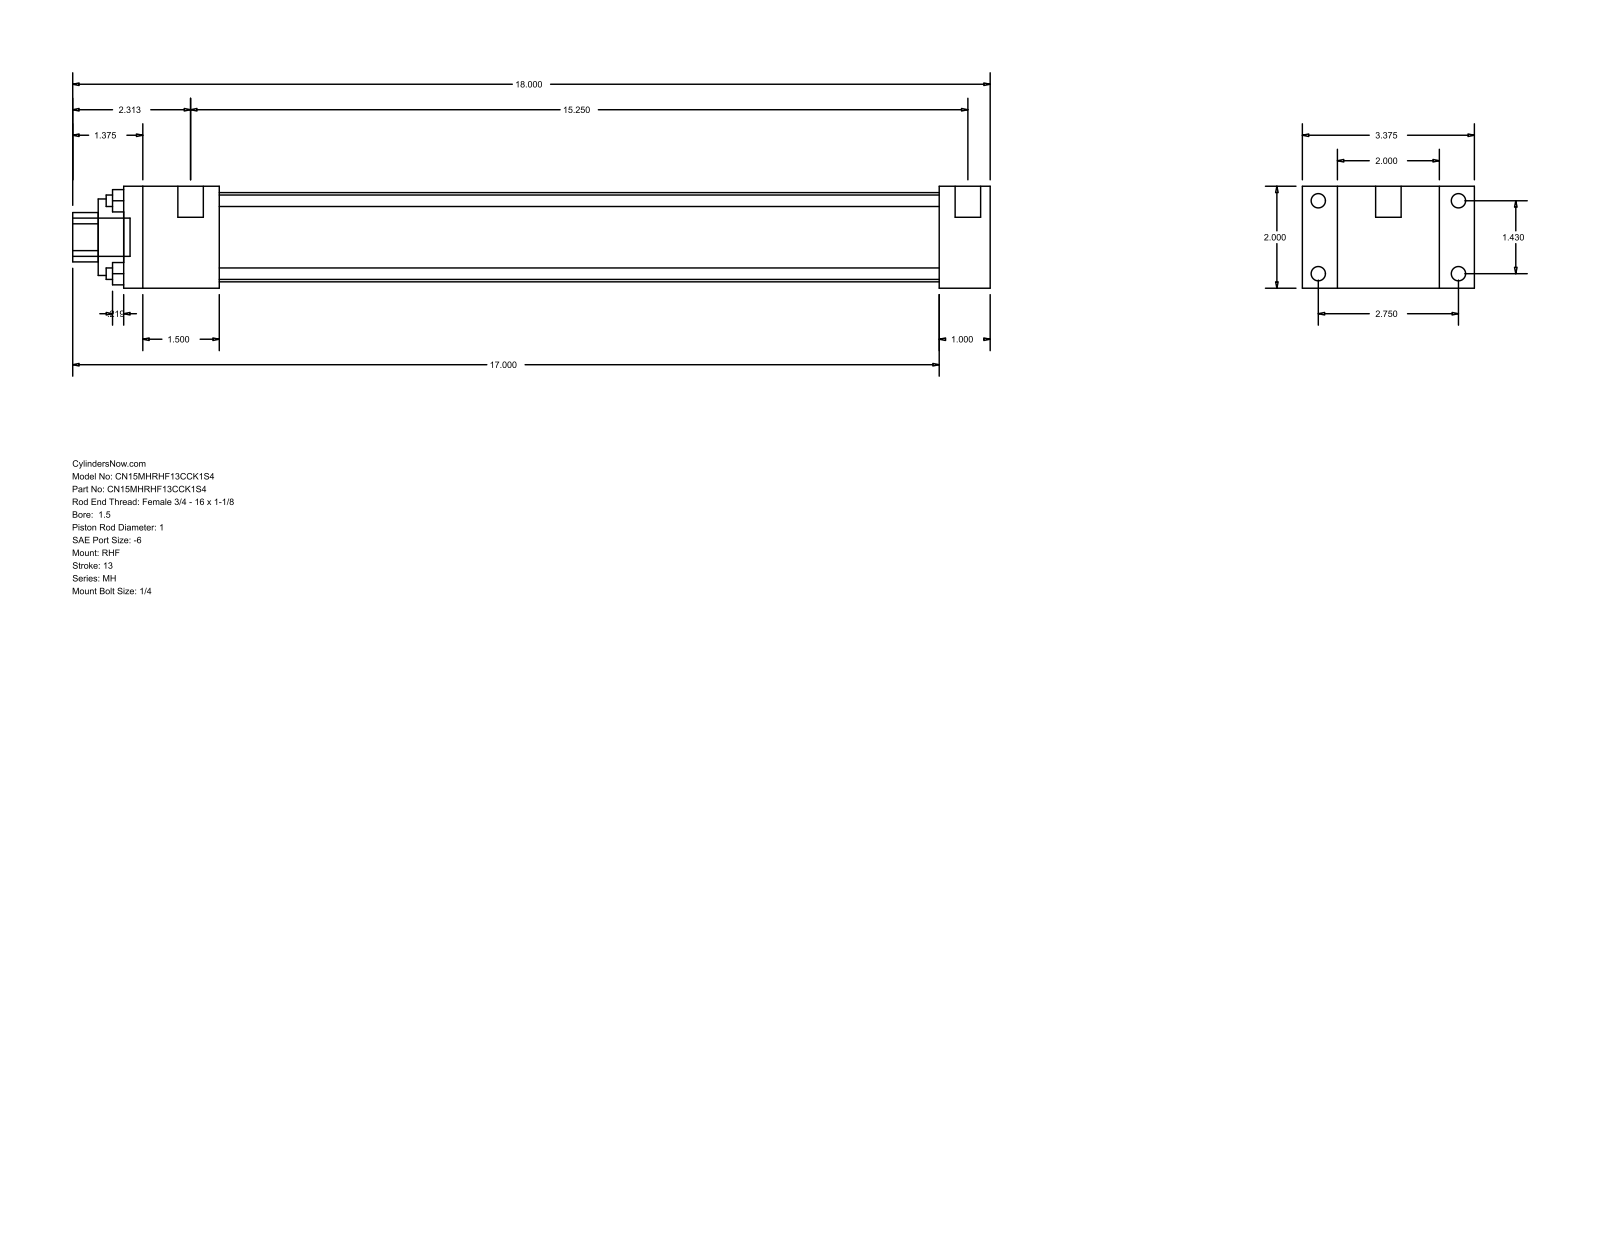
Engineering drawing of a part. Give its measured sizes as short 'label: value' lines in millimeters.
name: MH_RHF__0150_1
written by: GSSL Pune (CONFIG_CONTROL_DESIGN)
unit: mm
bodies: 0 solids, 88 faces (60 planar, 28 cylindrical, 0 other)
size: 457.2 × 85.72 × 50.8
holes: 4× ⌀5.71, 1× ⌀25.4, 1× ⌀38.1, 1× ⌀44.45
bosses: 4× ⌀7.14, 4× ⌀5.56, 2× ⌀12.7, 1× ⌀19.05
rounds: 1× R12.29
face distances: 50.8, 25.4, 17.46, 68.26, 85.72, 431.8, 406.4, 47.63, 358.77, 384.17
hole spacings: 25.68, 36.32, 51.36
